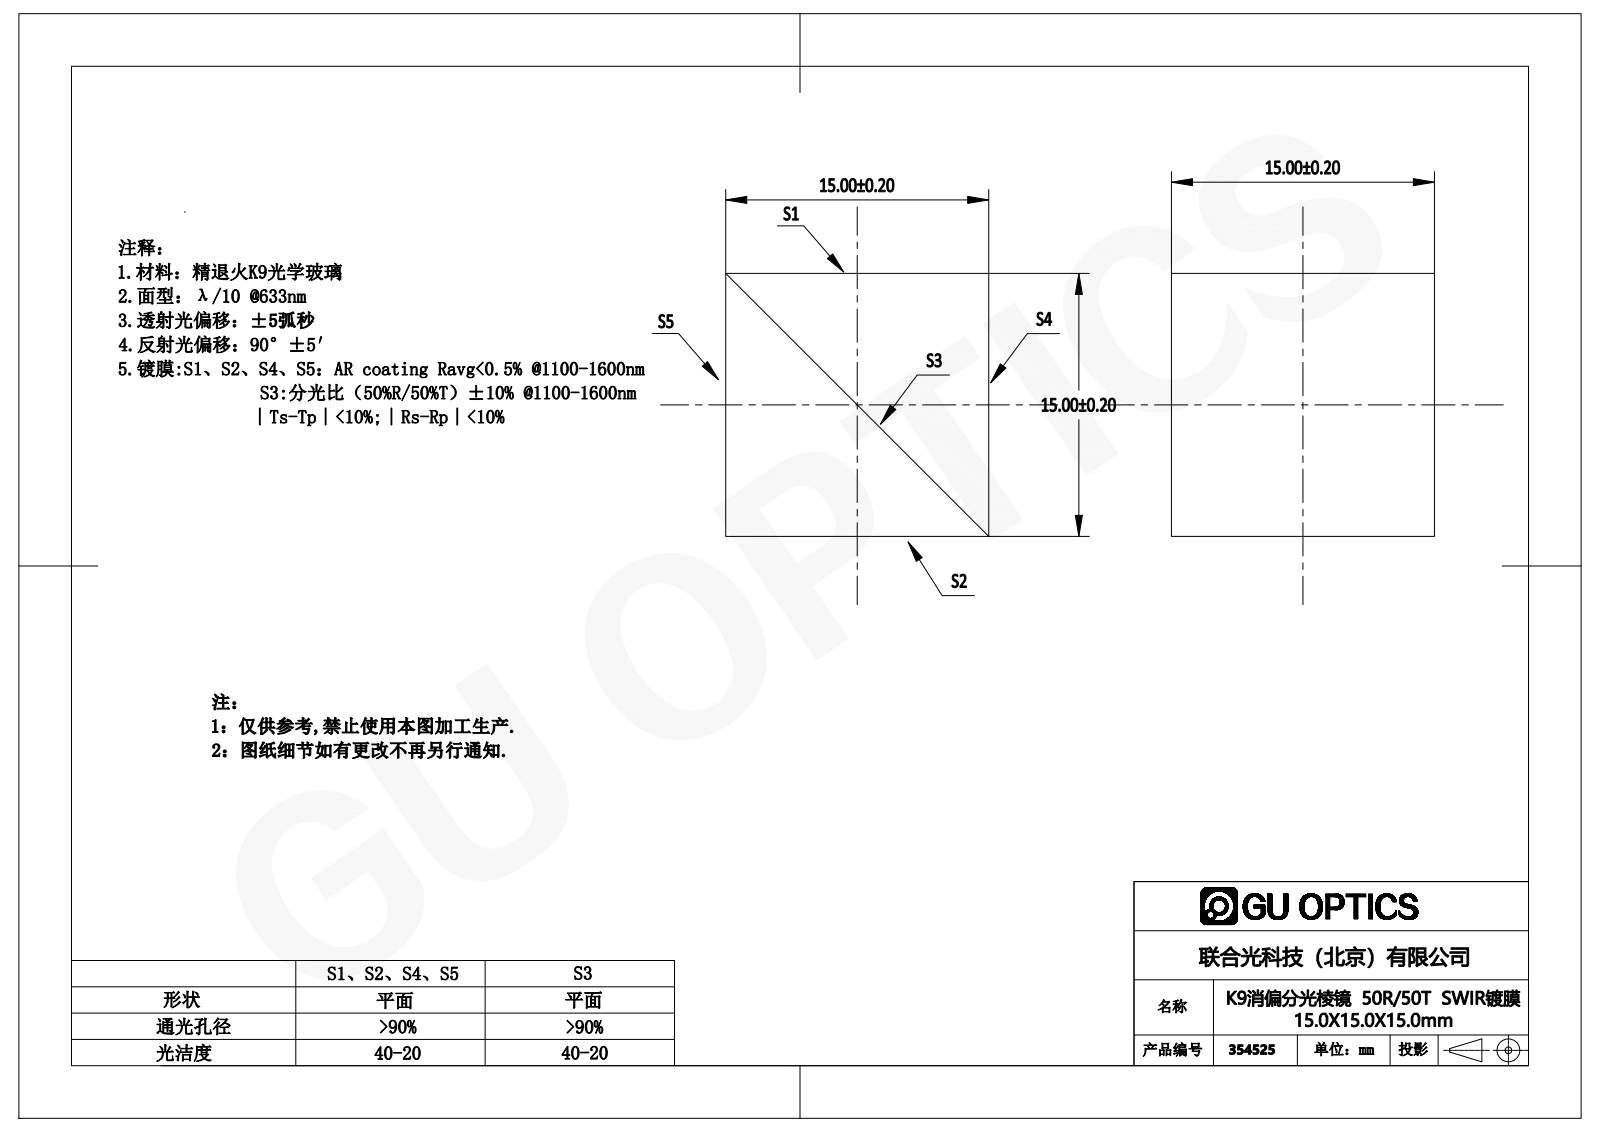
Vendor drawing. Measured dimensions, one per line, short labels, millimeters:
name: 352509
written by: SolidWorks 2016 (AUTOMOTIVE_DESIGN)
unit: mm
bodies: 2 solids, 10 faces (10 planar, 0 cylindrical, 0 other)
size: 15 × 15 × 15
volume: 3 375 mm³; area: 1 986 mm²
face distances: 15
